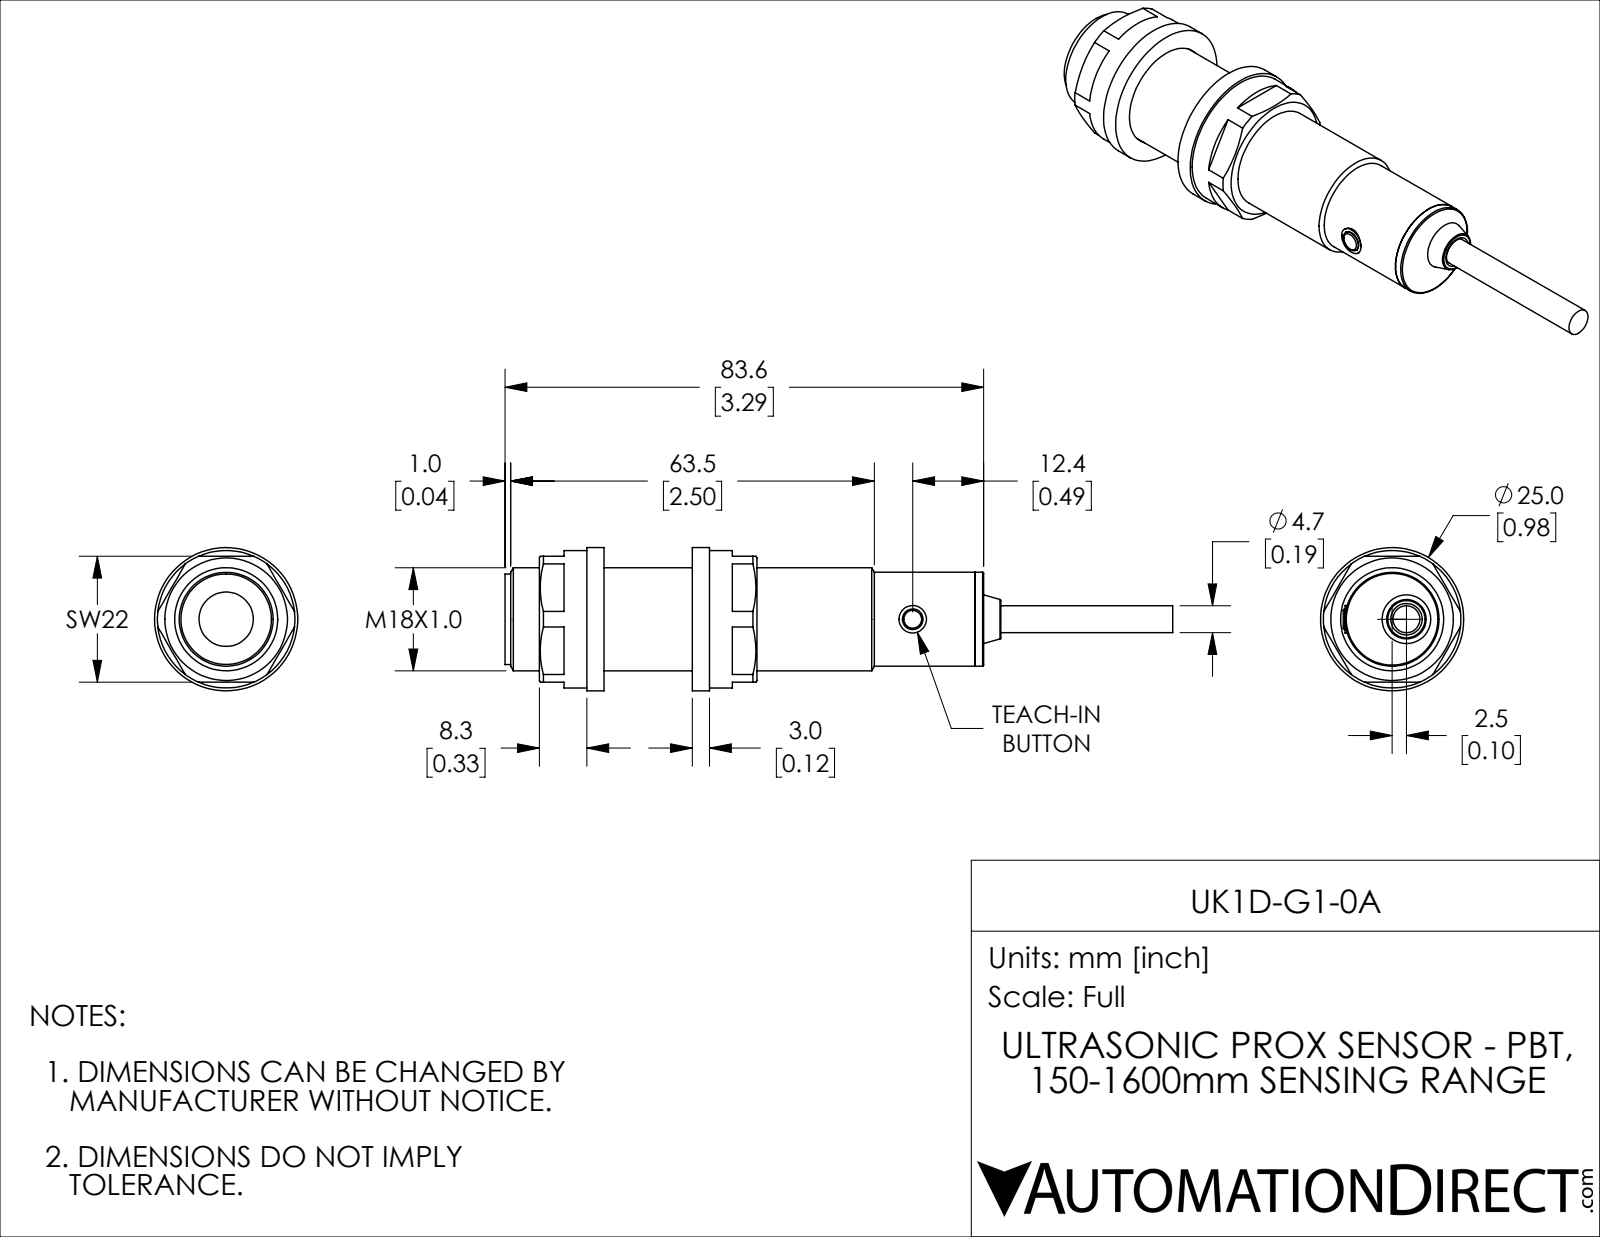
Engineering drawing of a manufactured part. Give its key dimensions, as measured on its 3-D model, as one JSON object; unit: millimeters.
{"part_name": "UK1D-G1-0A", "step_written_by": "SolidWorks 2018 (AUTOMOTIVE_DESIGN)", "units": "millimeters", "bodies": {"solids": 10, "faces": 107, "planar": 49, "cylindrical": 40, "other": 18}, "overall_size": [116.6, 25, 25], "volume_mm3": 25220, "surface_area_mm2": 11419, "round_holes": [[4.7, 2], [3.6, 1], [9.5, 1], [18, 1], [18.2, 1]], "round_bosses_or_shafts": [[25, 1], [24, 1], [16.4, 1], [15.8, 1], [5.4, 1], [4.8, 1]], "face_to_face_distances": [3, 18.4, 21.4, 67.8, 46.4, 13.3, 34.7, 81.1, 16.3, 64.8], "hole_center_spacings": [2.5]}
